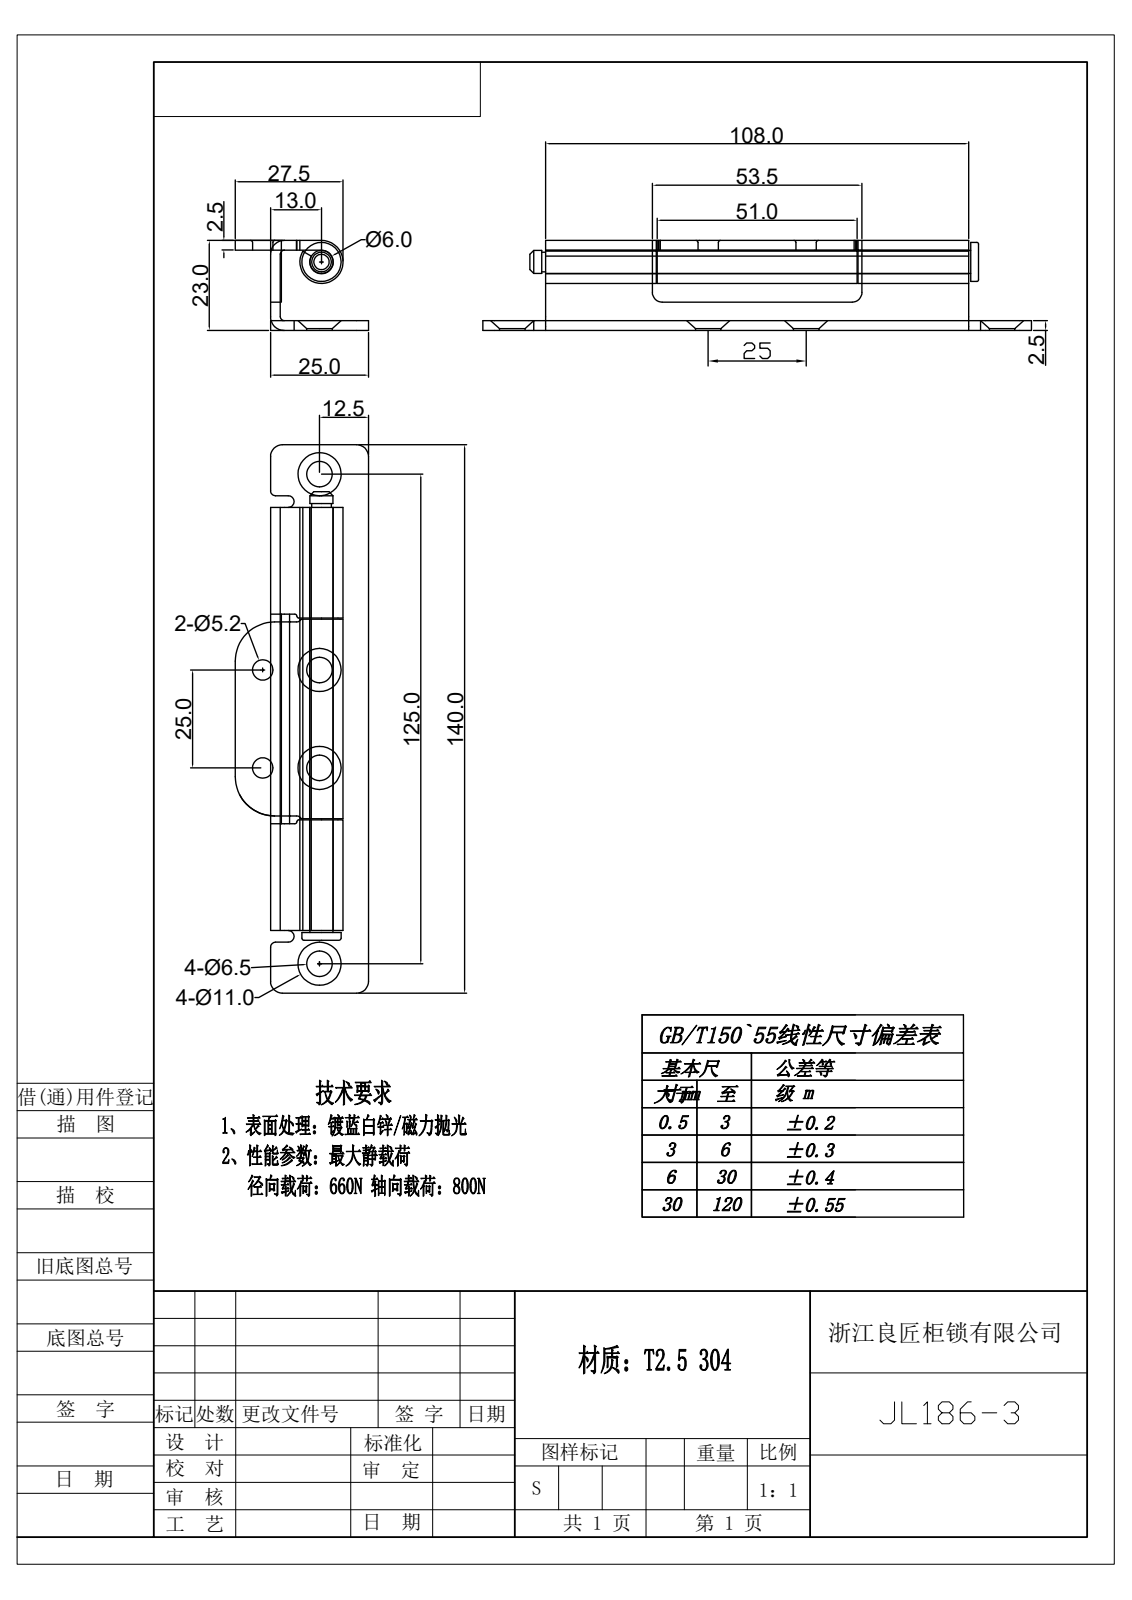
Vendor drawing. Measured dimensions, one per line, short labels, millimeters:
written by: Rhino 8.5 (CONFIG_CONTROL_DESIGN)
unit: mm
bodies: 3 solids, 125 faces (51 planar, 54 cylindrical, 20 other)
size: 140 × 34 × 23
volume: 24 615 mm³; area: 21 601 mm²
holes: 4× ⌀6.5, 2× ⌀5.2, 1× ⌀6
bosses: 1× ⌀11, 1× ⌀10, 1× ⌀5.9, 1× ⌀5
rounds: 4× R0.5, 4× R1, 4× R3, 2× R1.25, 2× R2.5, 2× R3.5, 2× R10
face distances: 2.5, 20.5, 18, 23, 25, 22.5, 13.5, 28.25, 79.75, 108
hole spacings: 14.5, 25, 28.9, 50, 52.06, 75, 76.39, 125
